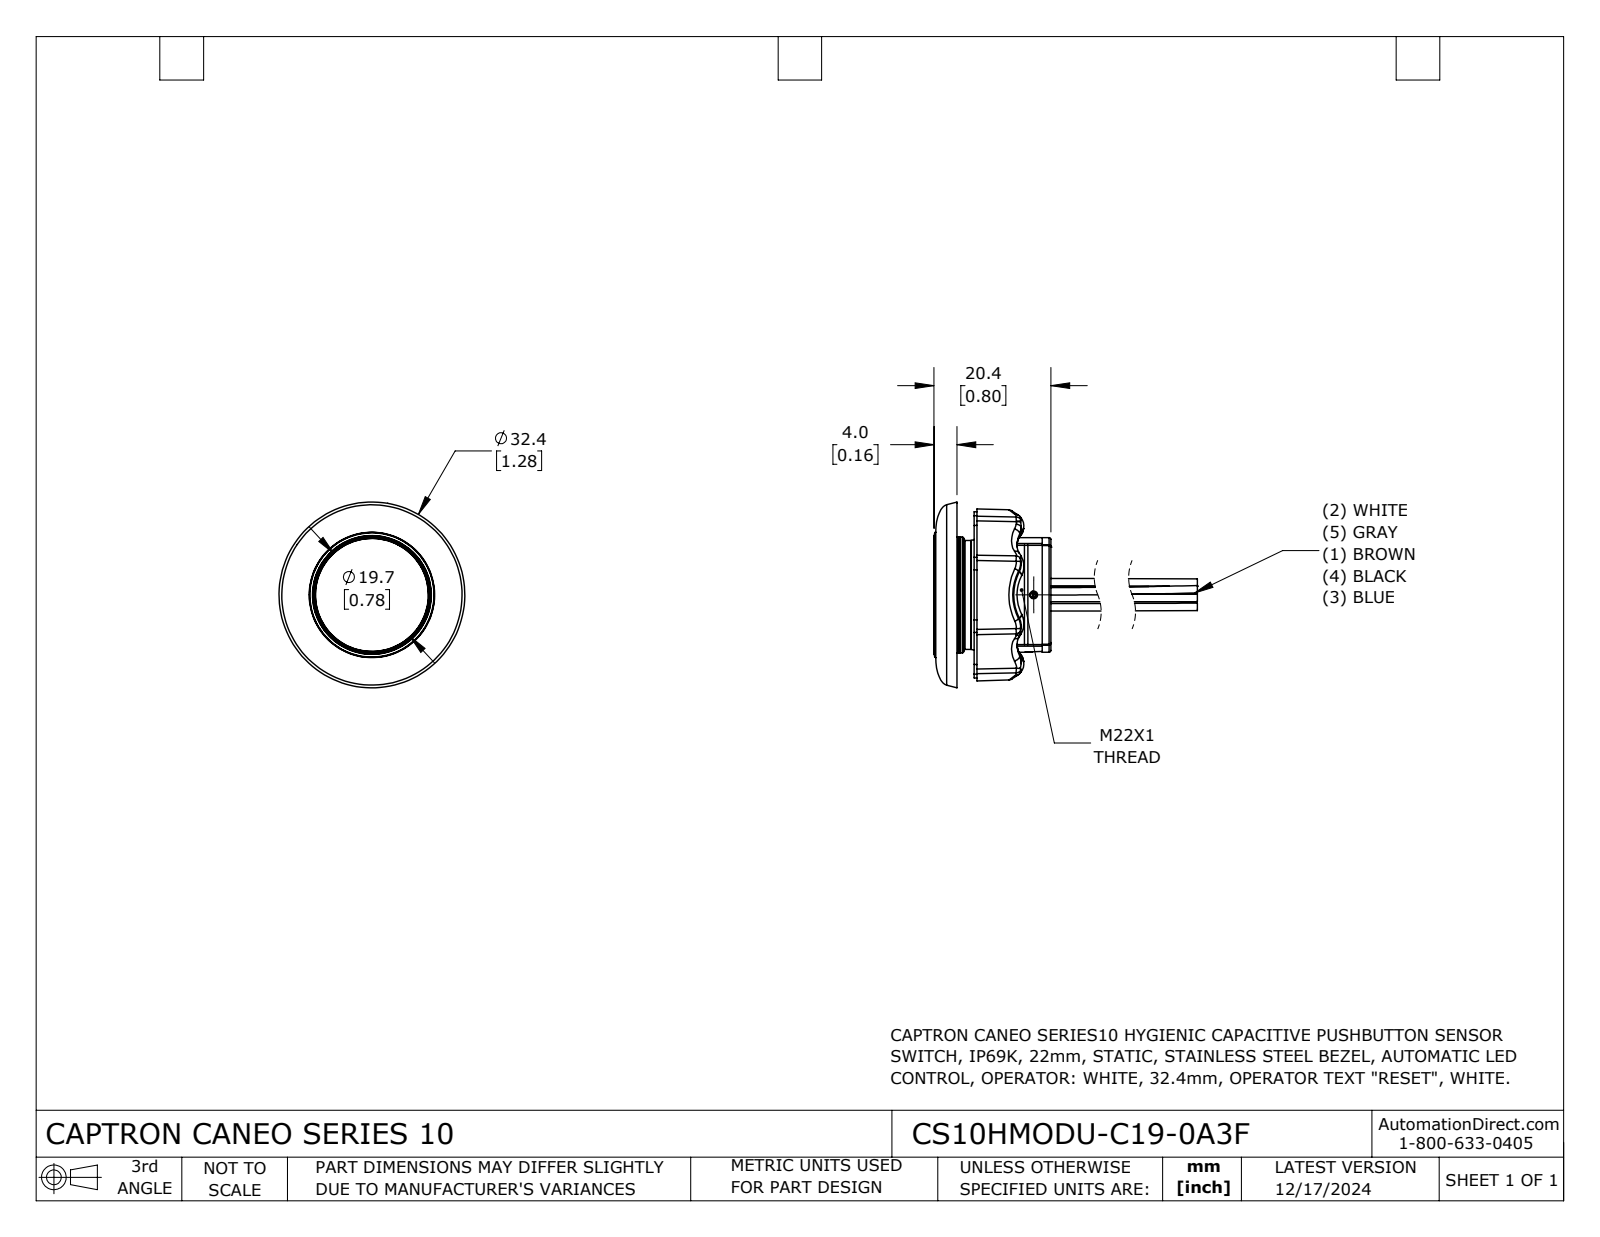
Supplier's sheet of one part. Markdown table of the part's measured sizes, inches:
| quantity | value |
| --- | --- |
| part name | CS10HMODU-C19-0A3F |
| STEP written by | SolidWorks 2024 (CONFIG_CONTROL_DESIGN) |
| units | inches |
| bodies | 7 solids, 854 faces (403 planar, 138 cylindrical, 313 other) |
| overall size | 1.803 × 1.277 × 1.277 |
| volume | 0.636 in³ |
| surface area | 9.99 in² |
| round holes (diameter × count) | 0.053 × 1, 0.827 × 1, 0.927 × 1, 1.004 × 1 |
| round bosses / shafts (diameter × count) | 0.748 × 1, 0.724 × 1 |
| partial cylindrical surfaces (radius × count) | 0.006 × 20, 0.004 × 6, 0.118 × 6, 0.295 × 6, 0.012 × 4, 0.039 × 4, 0.689 × 4, 0.196 × 1 |
| main face-to-face distances | 0.157, 0.646, 0.803, 0.134, 0.016, 0.528, 0.142, 0.118, 0.276, 0.661 |
